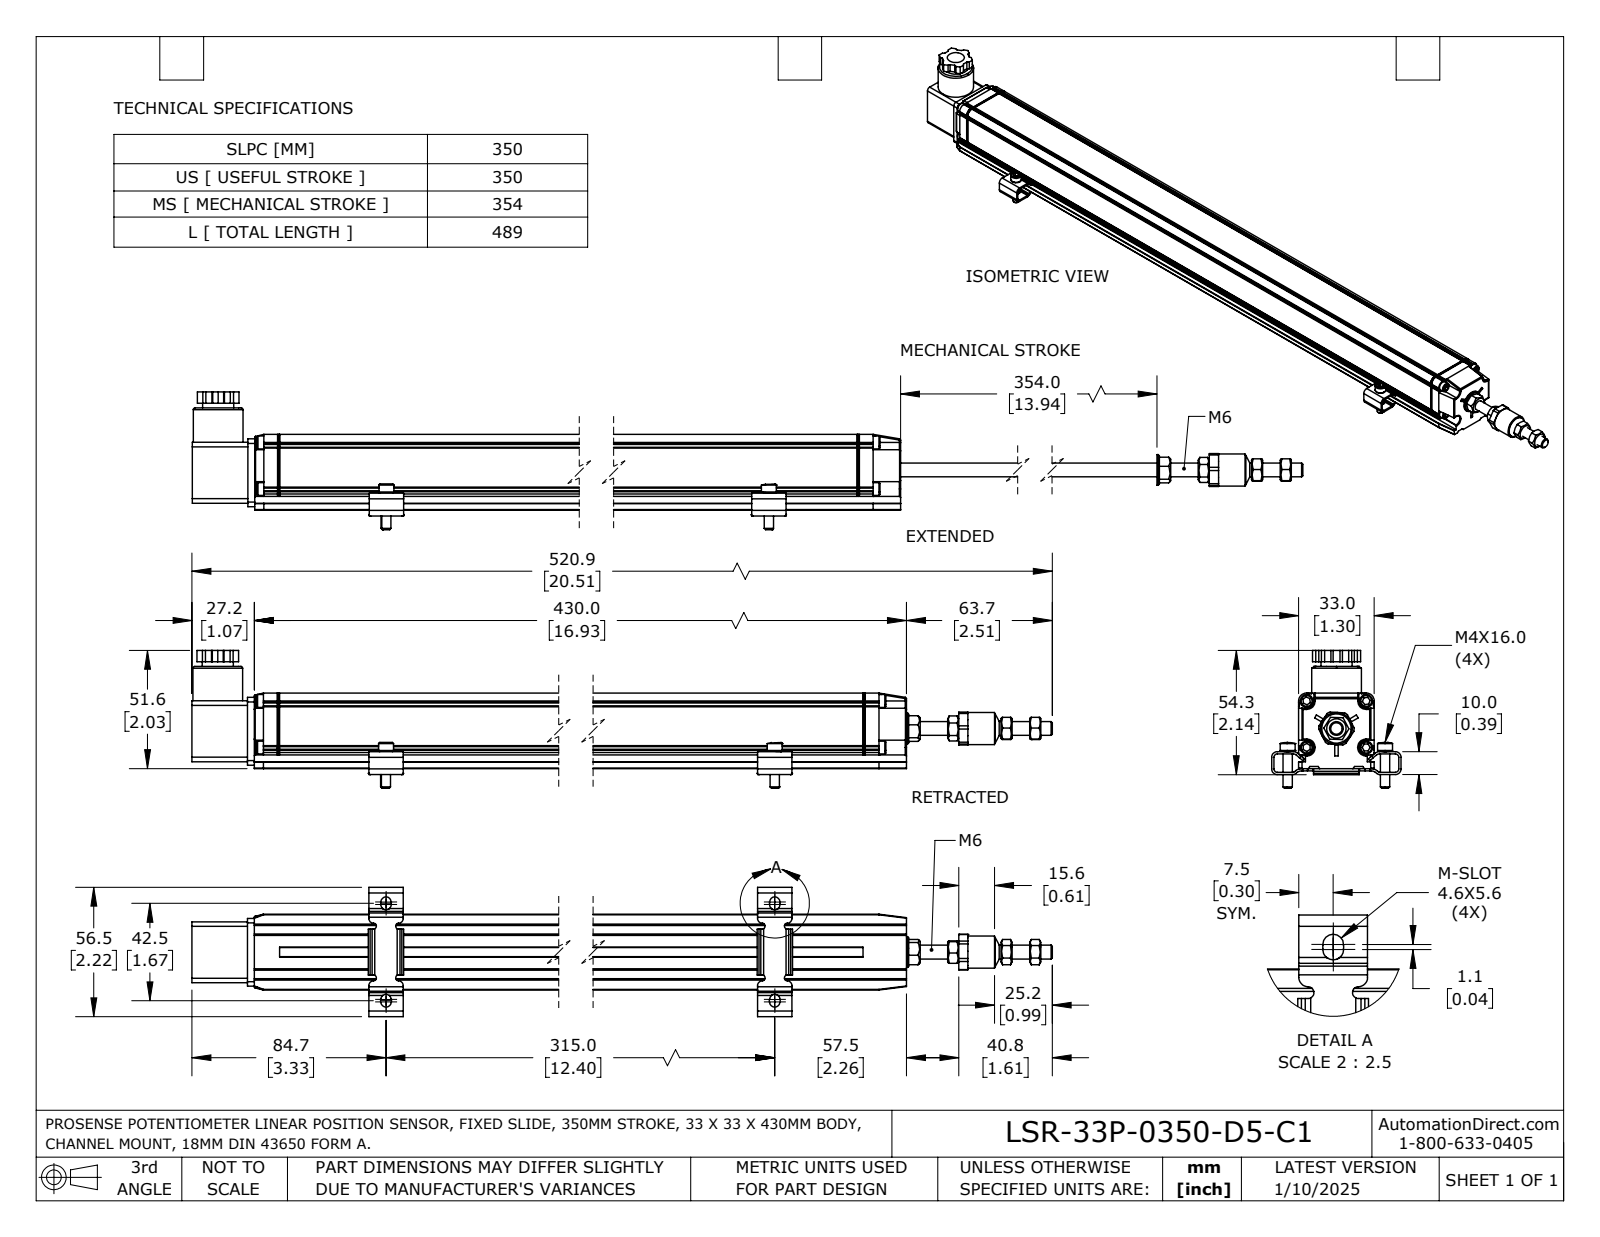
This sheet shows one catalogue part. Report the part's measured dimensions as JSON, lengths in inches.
{"part_name": "LSR-33P-0350-D5-C1", "step_written_by": "SolidWorks 2023 (AUTOMOTIVE_DESIGN)", "units": "inches", "bodies": {"solids": 14, "faces": 995, "planar": 641, "cylindrical": 269, "other": 85}, "overall_size": [20.506, 2.37, 2.224], "volume_in3": 26.92, "surface_area_in2": 177.7, "round_holes": [[0.106, 4], [0.13, 4], [0.169, 1], [0.205, 1], [0.209, 1], [0.232, 1], [0.276, 1], [0.285, 1], [0.394, 1], [0.413, 1], [0.573, 1], [0.602, 1]], "round_bosses_or_shafts": [[0.157, 5], [0.118, 5], [0.256, 4], [0.22, 4], [0.854, 1], [0.551, 1], [0.535, 1], [0.528, 1]], "partial_cylinders_radius": [[0.079, 28], [0.02, 23], [0.008, 16], [0.051, 8], [0.059, 8], [0.089, 8], [0.118, 8], [0.039, 4]], "face_to_face_distances": [1.299, 0.118, 0.22, 0.039, 1.181, 1.079, 0.079, 0.142, 0.102, 0.185], "hole_center_spacings": [0.047, 0.583, 0.607, 0.696, 0.73, 0.799, 1.024, 1.299]}
